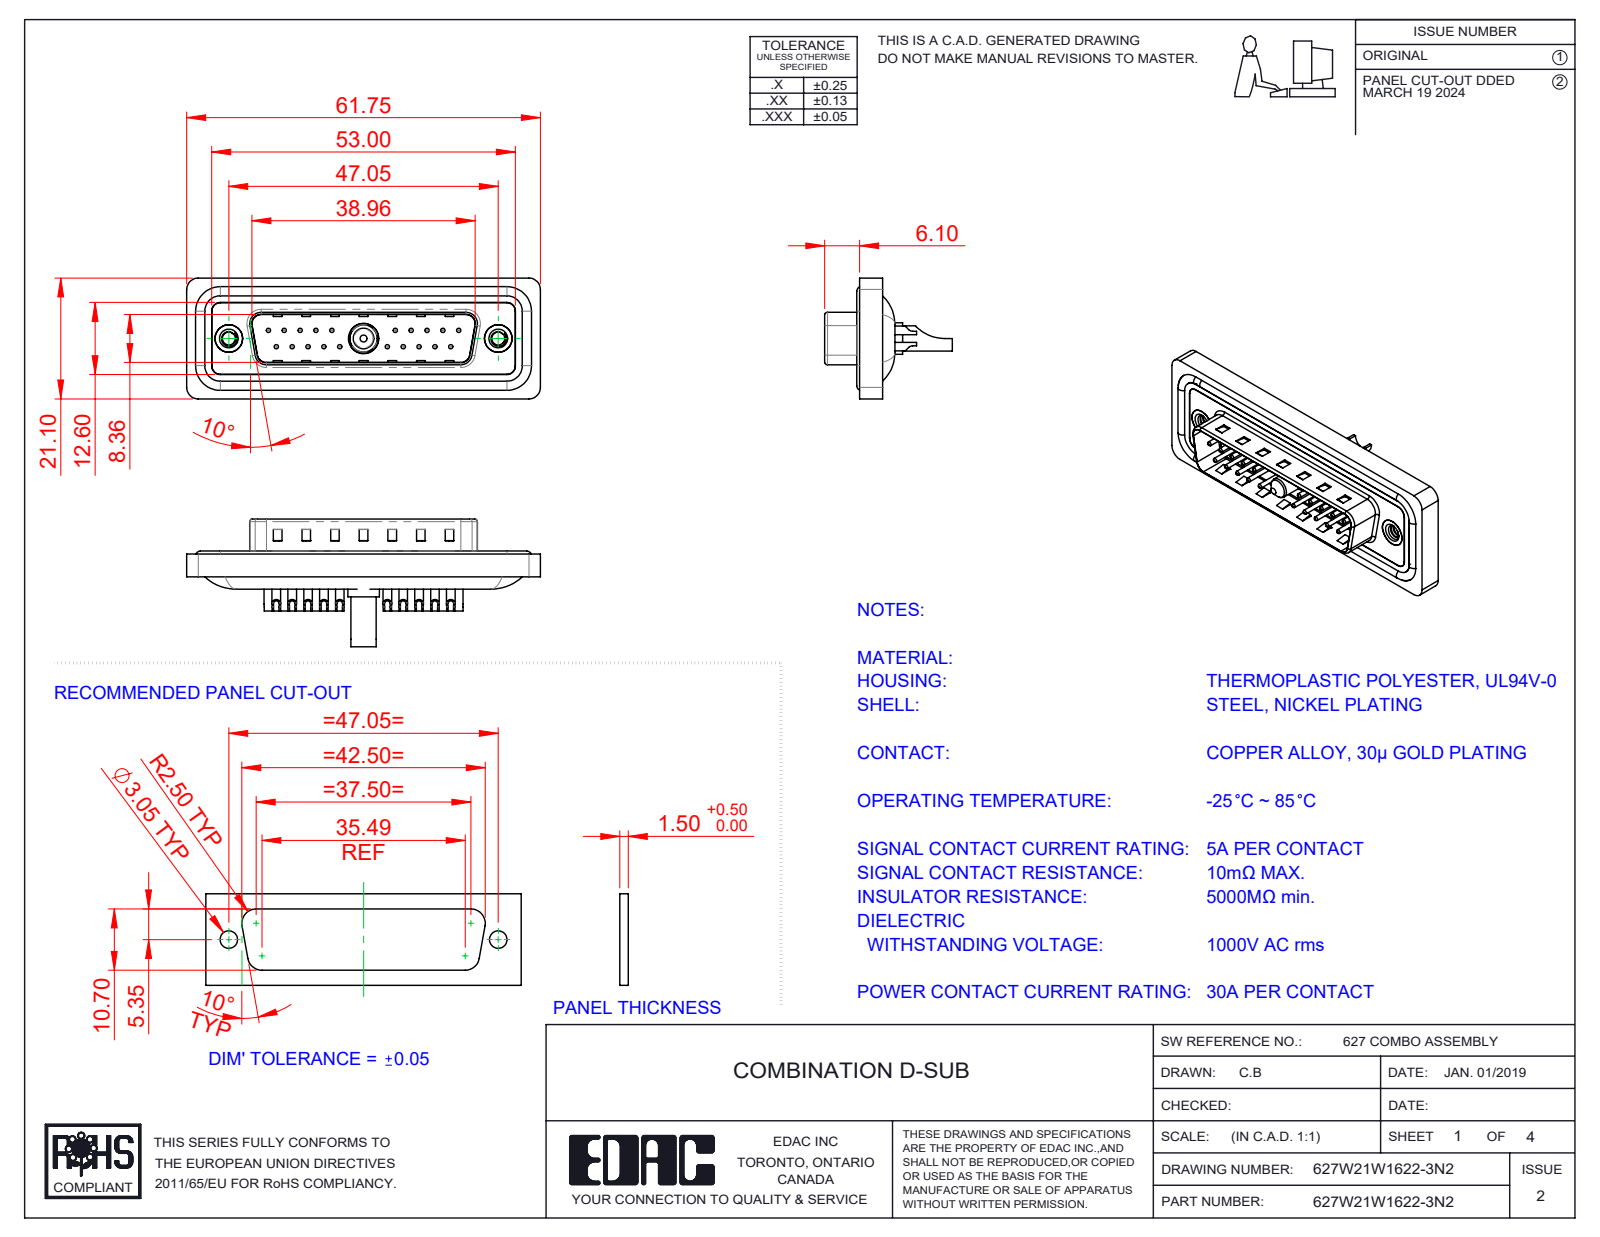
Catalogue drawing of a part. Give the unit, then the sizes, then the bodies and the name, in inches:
Units: inches
Overall size (bounding box): 2.431 × 0.878 × 0.831
Round holes (diameter × count): ⌀0.03 ×20, ⌀0.039 ×20, ⌀0.063 ×20, ⌀0.079 ×20, ⌀0.089 ×2, ⌀0.157 ×2, ⌀0.189 ×2, ⌀0.197 ×2, ⌀0.138 ×1, ⌀0.191 ×1, ⌀0.209 ×1
Round bosses / shafts (diameter × count): ⌀0.059 ×20, ⌀0.063 ×4, ⌀0.193 ×2, ⌀0.217 ×1, ⌀0.205 ×1, ⌀0.187 ×1, ⌀0.173 ×1, ⌀0.148 ×1
Partial cylindrical surfaces — rounded edges, fillets, slot ends (radius × count): R0.059 ×22, R0.079 ×18, R0.02 ×8, R0.063 ×8, R0.039 ×6, R0.01 ×4, R0.024 ×4, R0.026 ×4
Main face-to-face distances: 0.016, 0.059, 0.043, 0.063, 0.02, 0.122, 0.114, 0.161, 0.032, 0.377
Hole centre spacings: 0.124, 0.109, 0.218, 0.327, 0.198, 0.763, 0.826, 0.872
Volume: 0.443 in³ · Surface area: 18.94 in²
Bodies: 29 solids, 1268 faces (402 planar, 530 cylindrical, 336 other)
Part name (STEP PRODUCT): Power Pin_30A SC; 627Combo Threaded Rivet_2; 627Combo Waterproof Housing_25 Contacts; 627Combo Shell Front_25 Contacts (+5 more)
STEP written by: SolidWorks 2023 (CONFIG_CONTROL_DESIGN)
